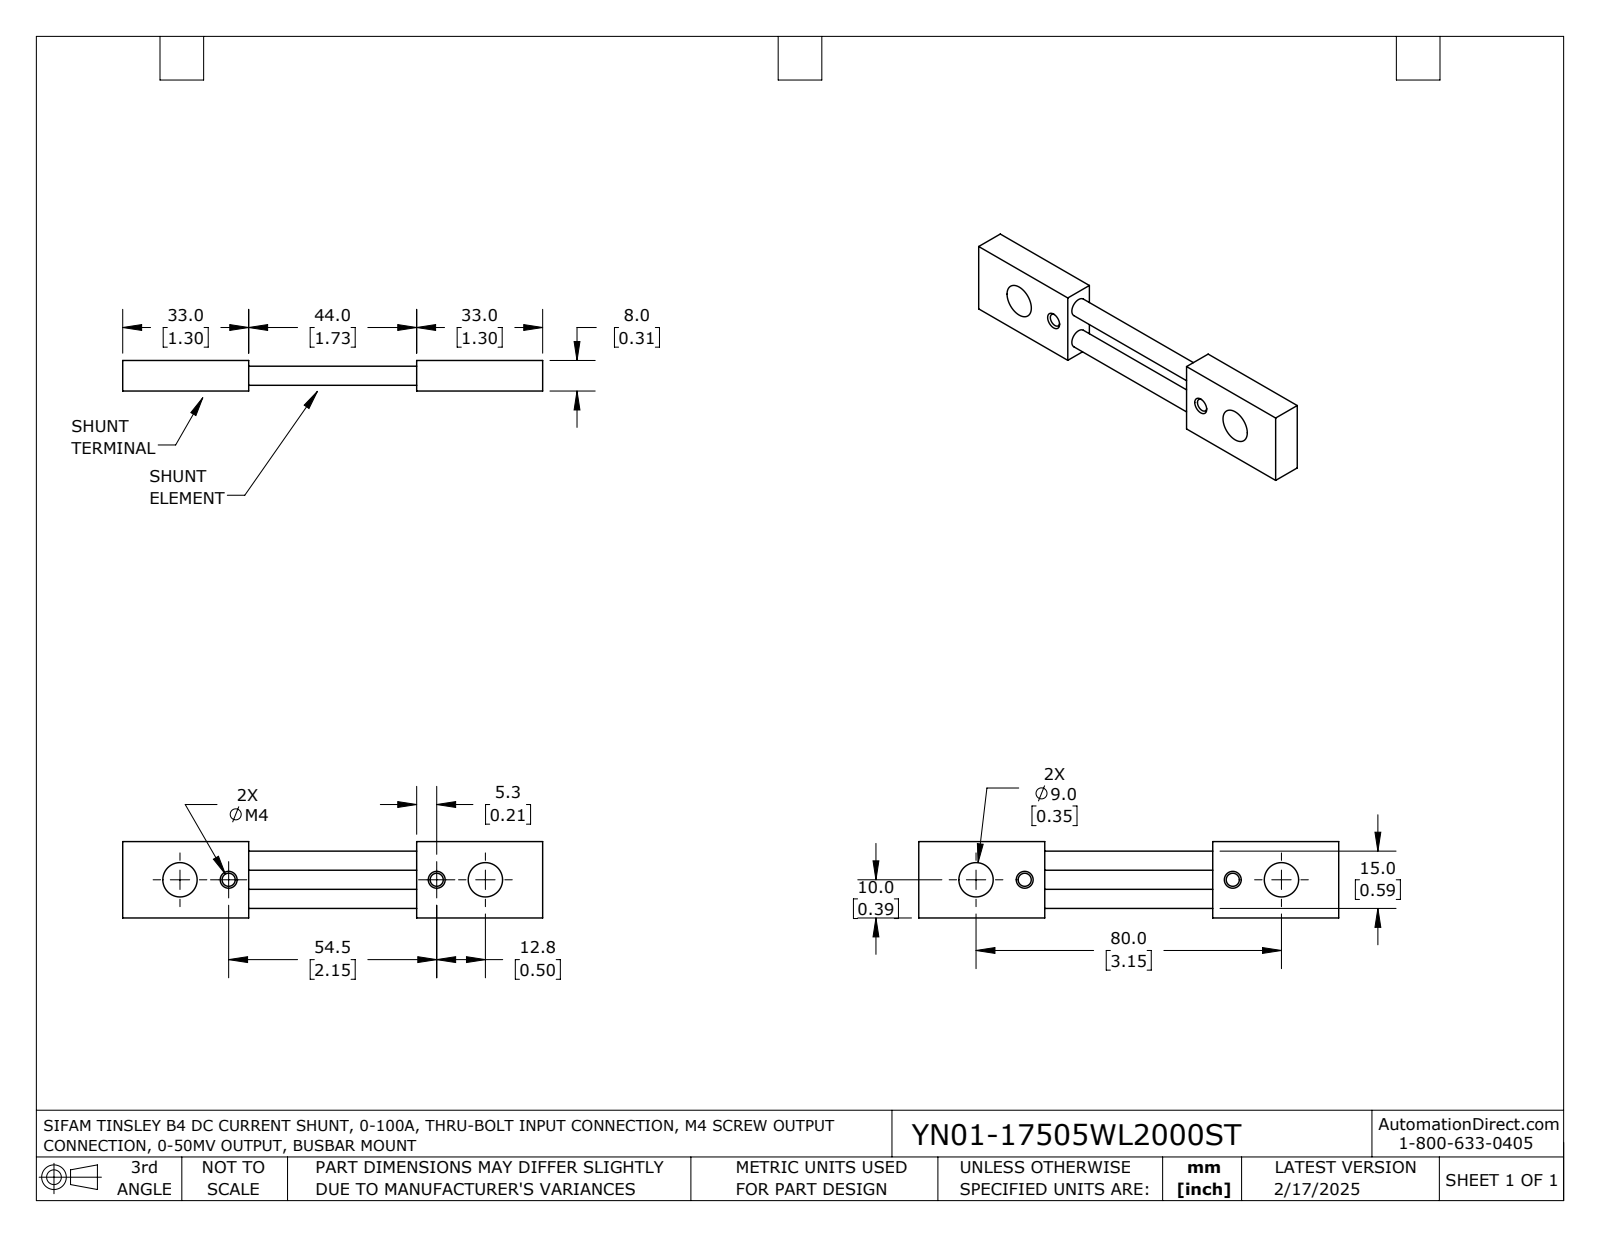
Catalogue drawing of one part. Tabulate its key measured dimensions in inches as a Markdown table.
| quantity | value |
| --- | --- |
| part name | YN01-17505WL2000ST |
| STEP written by | SolidWorks 2021 (AUTOMOTIVE_DESIGN) |
| units | inches |
| bodies | 1 solid, 48 faces (20 planar, 20 cylindrical, 8 other) |
| overall size | 4.331 × 0.787 × 0.315 |
| volume | 0.677 in³ |
| surface area | 9.504 in² |
| round holes (diameter × count) | 0.135 × 2, 0.197 × 2, 0.354 × 2 |
| main face-to-face distances | 0.315, 0.787, 1.299, 3.031, 4.331, 1.732, 1.094, 1.102, 3.228, 3.236 |
| hole center spacings | 0.502, 2.648, 0.394, 2.146, 3.15 |
